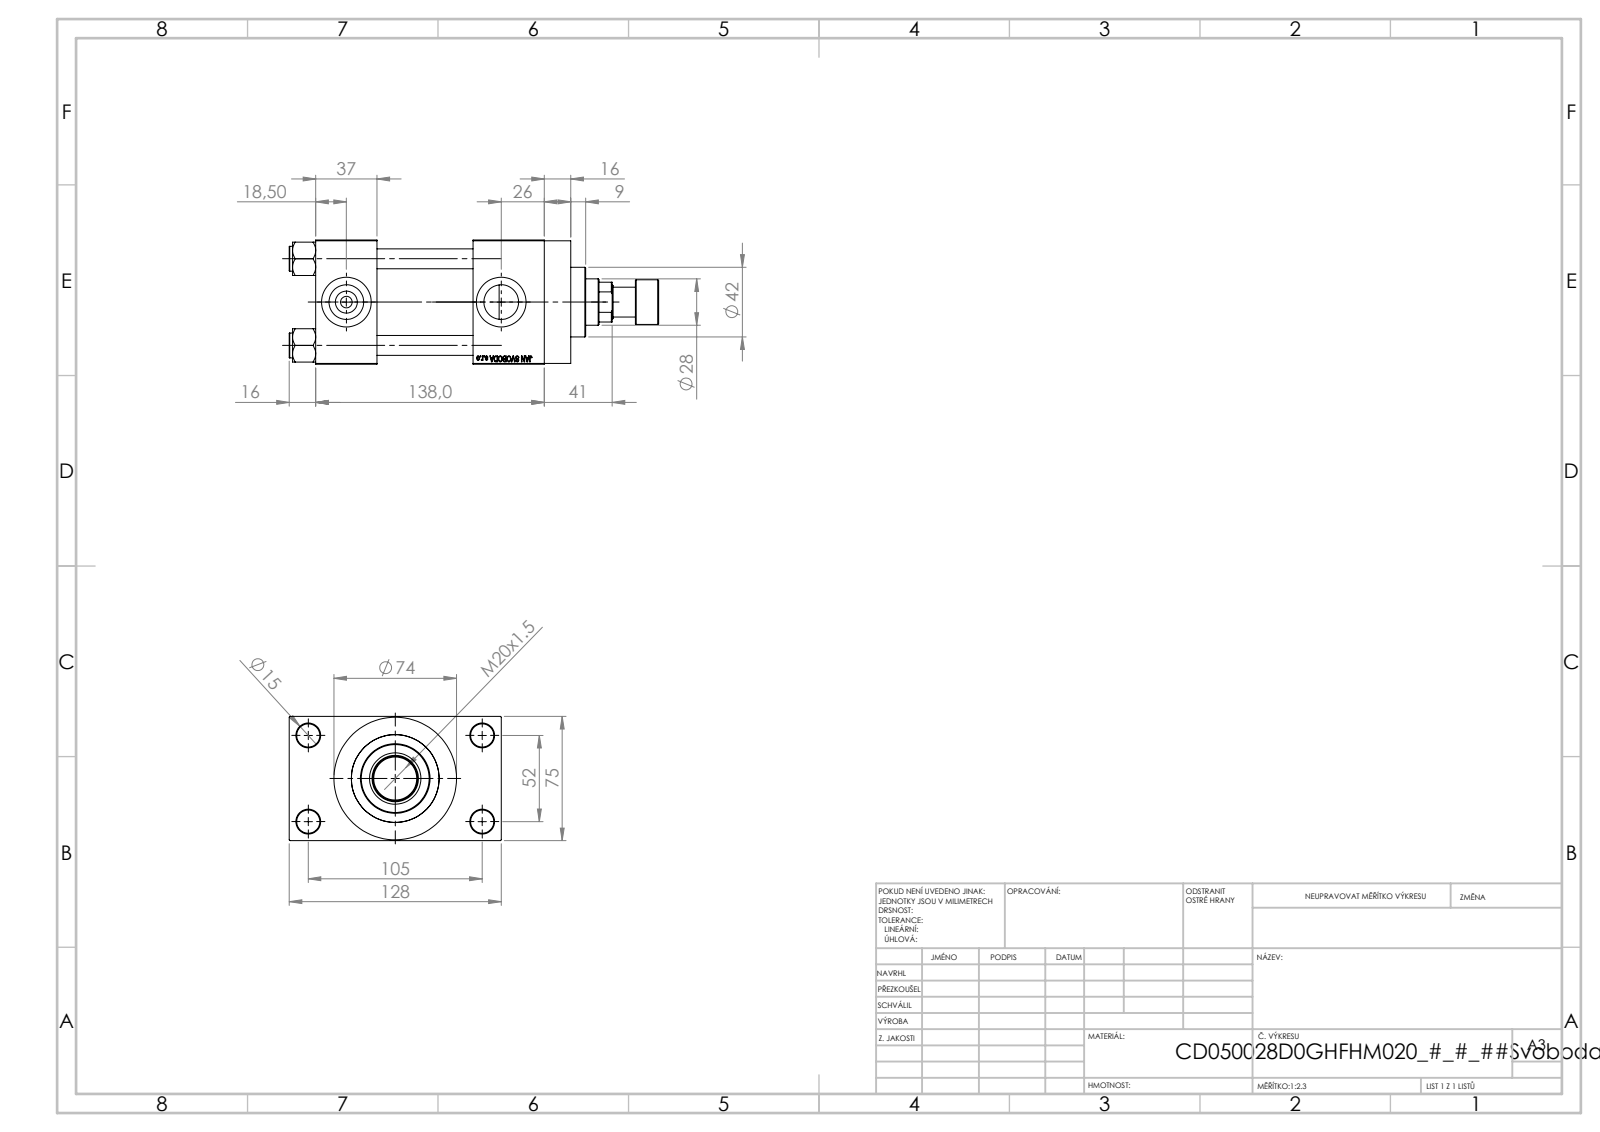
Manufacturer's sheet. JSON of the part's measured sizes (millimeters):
{"part_name": "V215CR_ROD_END_F; V215CD_NUT_M5_D; V215CD_D_Body; V215CD_VC_A (+2 more)", "step_written_by": "SolidWorks 2019 (CONFIG_CONTROL_DESIGN)", "units": "millimeters", "bodies": {"solids": 12, "faces": 1117, "planar": 501, "cylindrical": 92, "other": 524}, "overall_size": [223, 128, 75], "volume_mm3": 817817, "surface_area_mm2": 173865, "round_holes": [[12, 4], [14, 4], [7, 2], [20.96, 2], [30, 2], [18.5, 1], [28, 1], [31, 1], [41, 1], [50, 1], [53, 1]], "round_bosses_or_shafts": [[15, 4], [74, 1], [56, 1], [42, 1], [27, 1], [18, 1]], "face_to_face_distances": [75, 58, 37, 95, 26.5, 138, 101, 43, 101.5, 16], "hole_center_spacings": [26.35, 36.98, 52.3, 58.43, 58.59, 78.65, 94.37, 52]}
